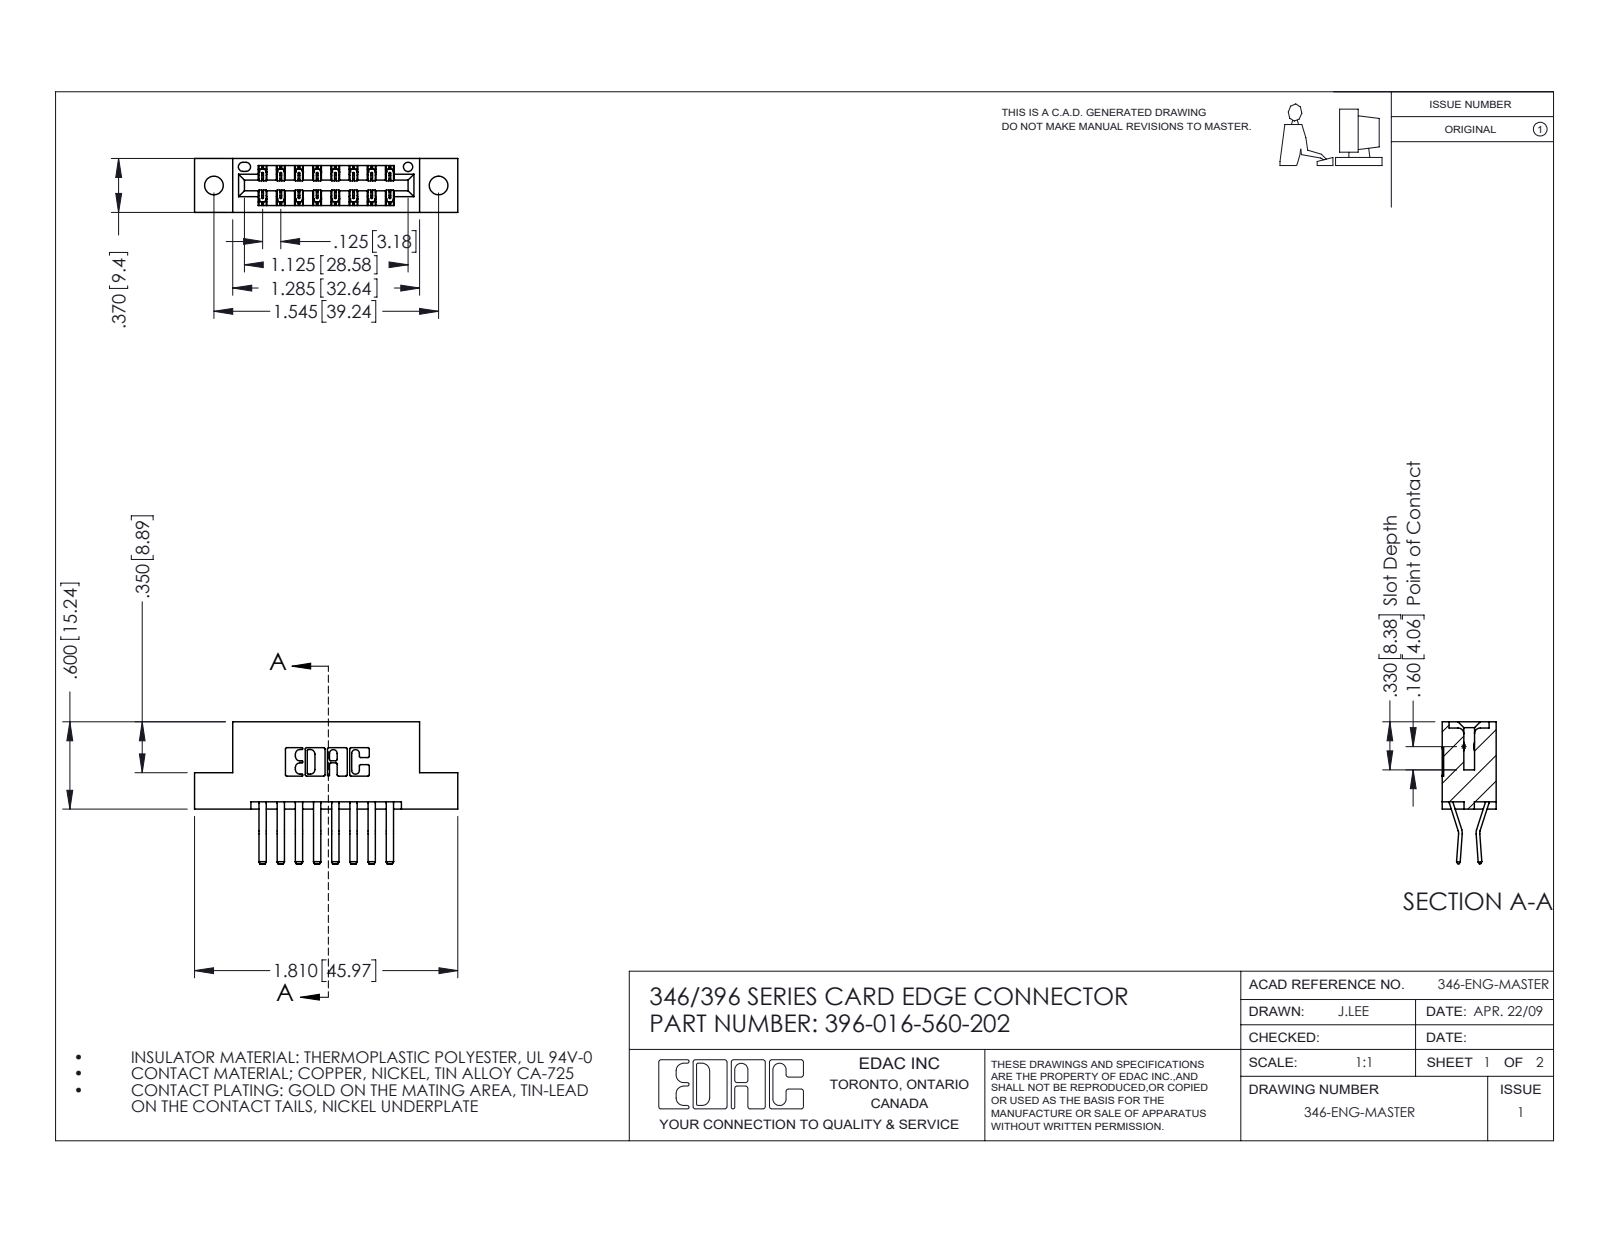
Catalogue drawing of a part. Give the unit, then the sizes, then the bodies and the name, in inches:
Units: inches
Overall size (bounding box): 1.81 × 0.975 × 0.37
Round holes (diameter × count): ⌀0.128 ×2, ⌀0.064 ×1
Partial cylindrical surfaces — rounded edges, fillets, slot ends (radius × count): R0.006 ×24, R0.01 ×22, R0.007 ×6, R0.031 ×6, R0.026 ×3, R0.01 ×2, R0.014 ×2, R0.022 ×2
Main face-to-face distances: 0.25, 0.048, 0.322, 0.37, 0.025, 0.5, 0.148, 0.222, 0.1, 0.174
Hole centre spacings: 0.246, 1.341, 1.545
Volume: 0.262 in³ · Surface area: 8.322 in²
Bodies: 17 solids, 986 faces (636 planar, 350 cylindrical, 0 other)
Part name (STEP PRODUCT): 396-016-560-202; 345-292-001_560 Tail; 346 Part_Flush Mounting Lugs - 0.128 Dia
STEP written by: SolidWorks 2016 (CONFIG_CONTROL_DESIGN)
